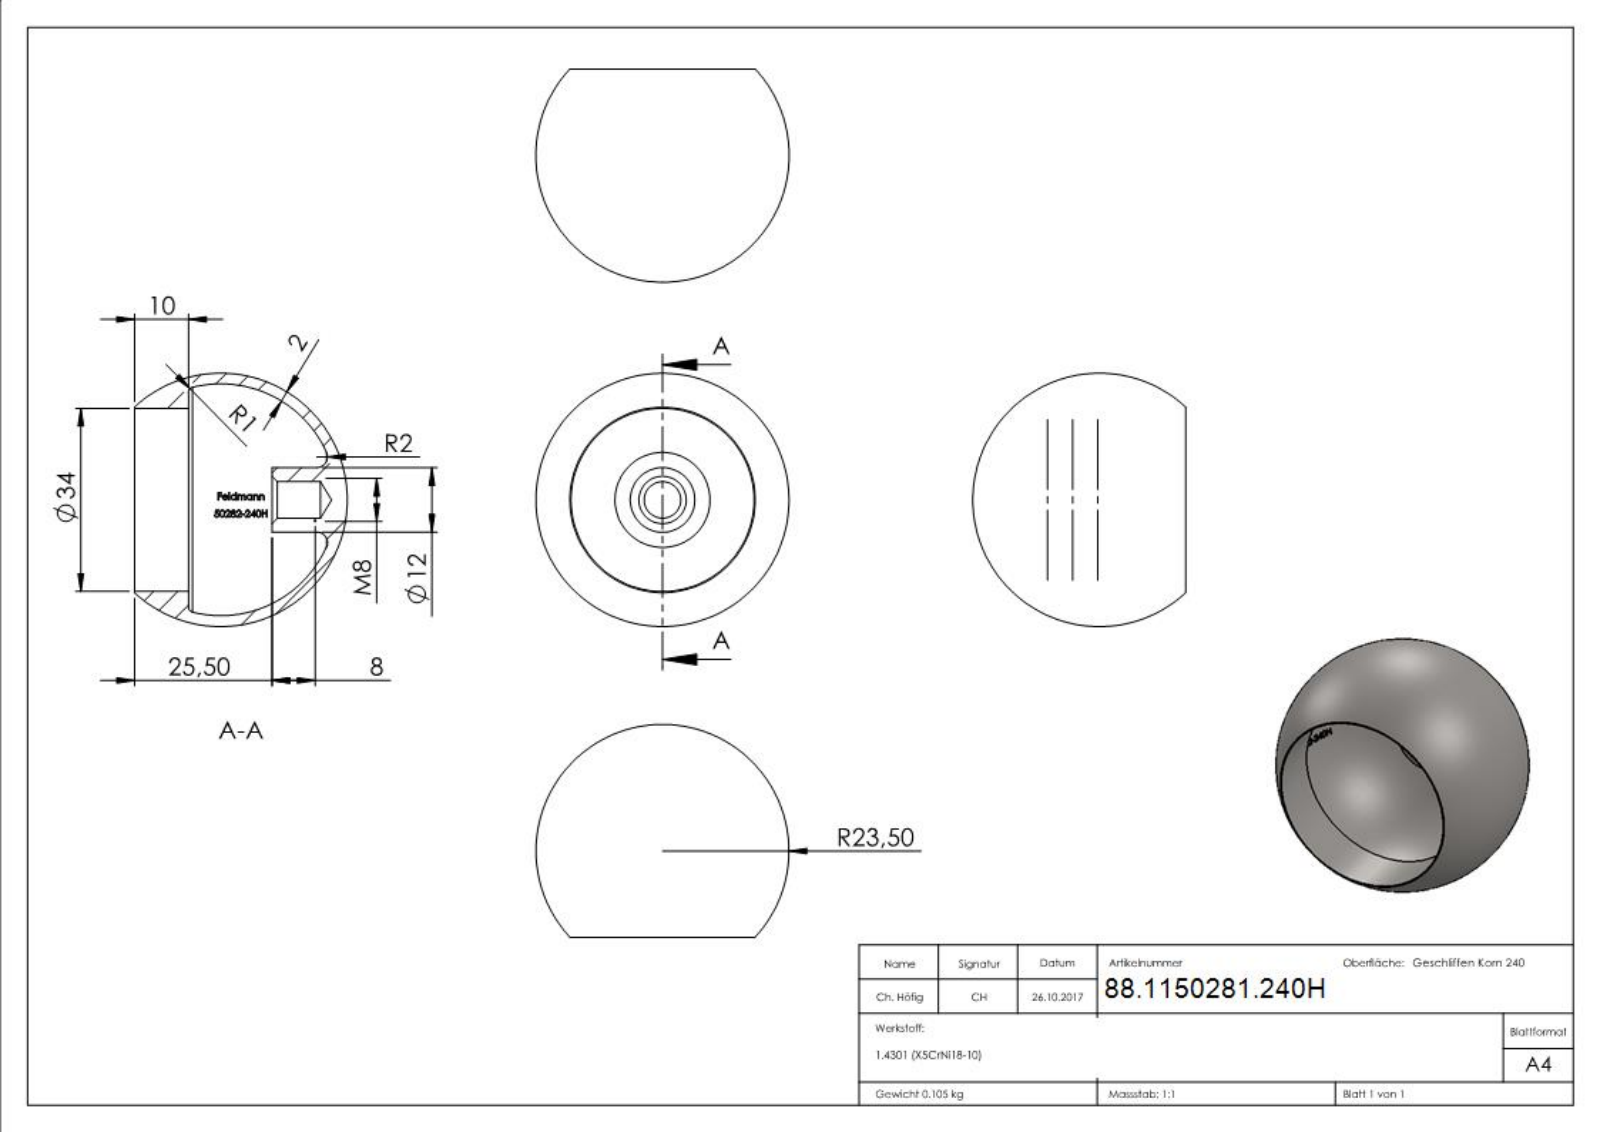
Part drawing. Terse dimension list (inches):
name: 50281-240H
written by: SolidWorks 2015 (CONFIG_CONTROL_DESIGN)
unit: in
bodies: 1 solid, 264 faces (110 planar, 6 cylindrical, 148 other)
size: 2.539 × 2.539 × 2.087
volume: 1.436 in³; area: 33.02 in²
holes: 1× ⌀0.268, 1× ⌀1.917
bosses: 1× ⌀0.472
face distances: 0.394, 1.142, 1.535, 0.226, 0.049, 0.126, 0.054, 0.08, 0.275, 0.243
